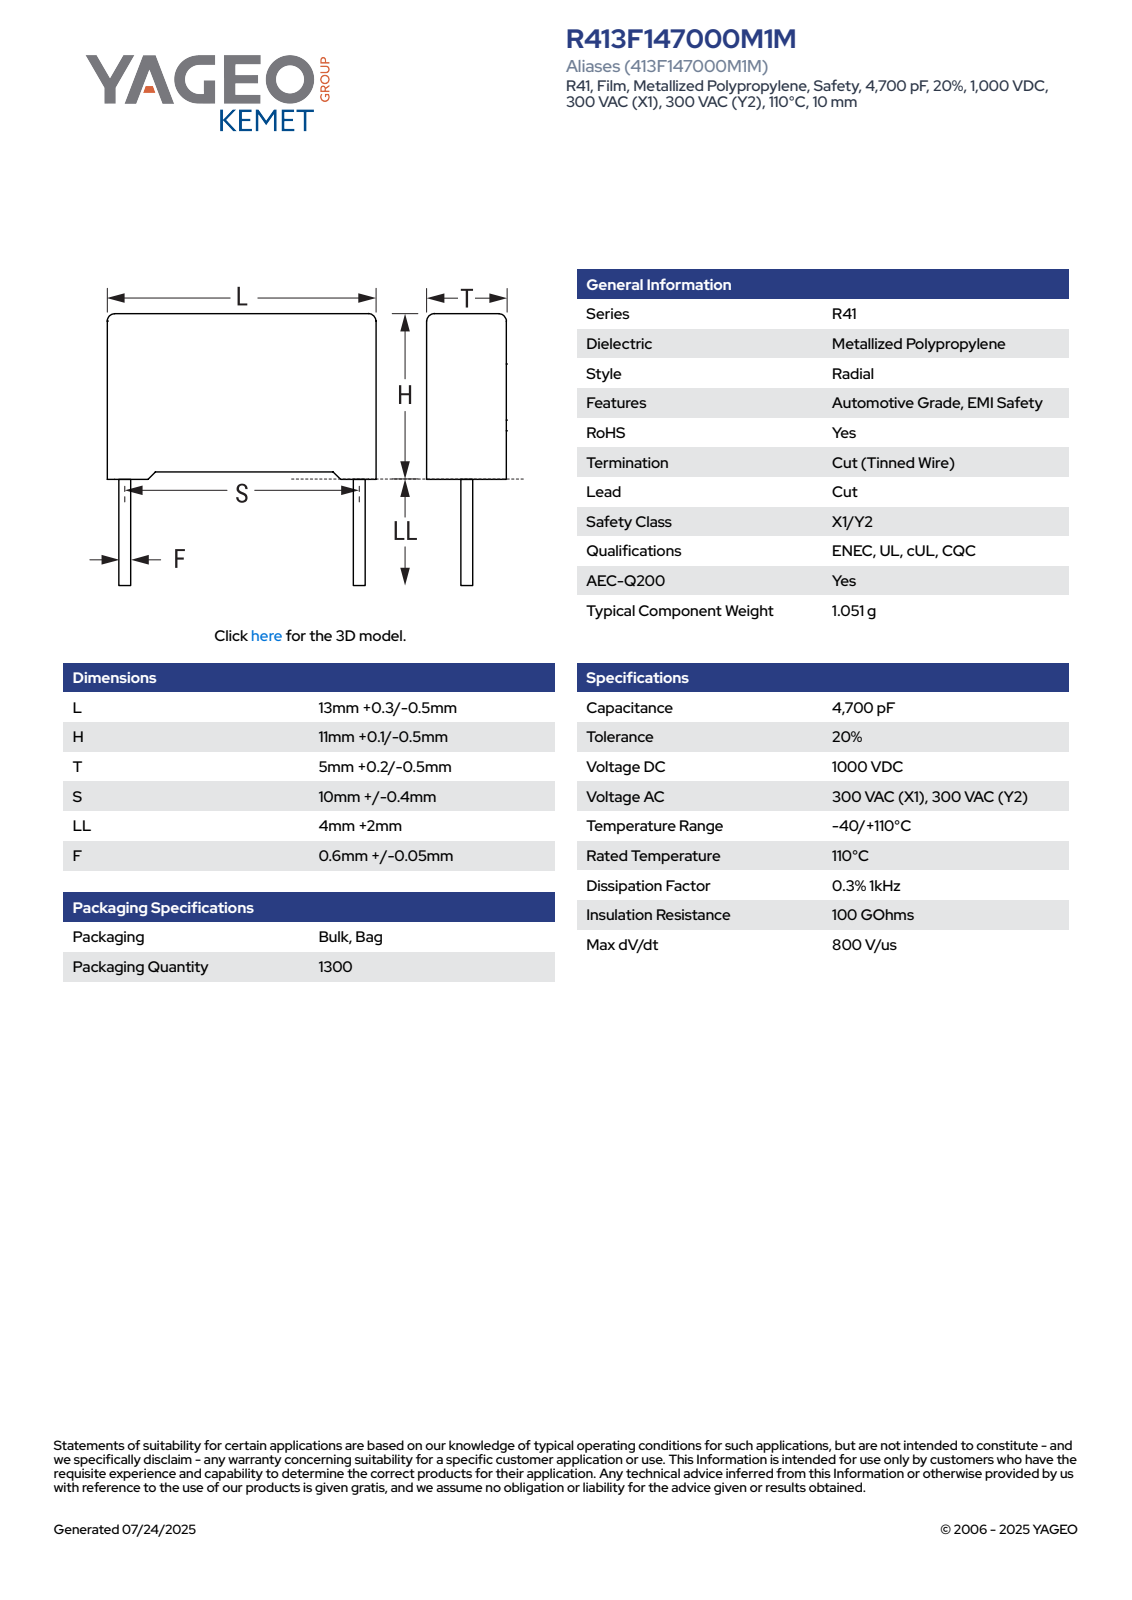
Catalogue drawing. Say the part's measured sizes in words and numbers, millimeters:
The part is named "CFR_RB2_13X11X5_L13.3H11.1T5.2S10LL6F0.65". Its 3-D file was written by "SolidWorks 2021 (AUTOMOTIVE_DESIGN)". It is 4 solids with 85 faces: 77 planar, 8 cylindrical and 0 other. Overall it measures 17.1 by 13.3 by 5.21 millimeters. Its volume is 728 cubic millimeters and its surface area 597 square millimeters. Round bosses or shafts: 2 of diameter 0.65. Partial cylindrical surfaces (rounded edges, fillets, slot ends): 4 of radius 0.5. The main face-to-face distances are 5.2, 13.3, 10.35, 0.44, 4.76, 0.75, 11.1, 4.32, 12.86, 0.37.
